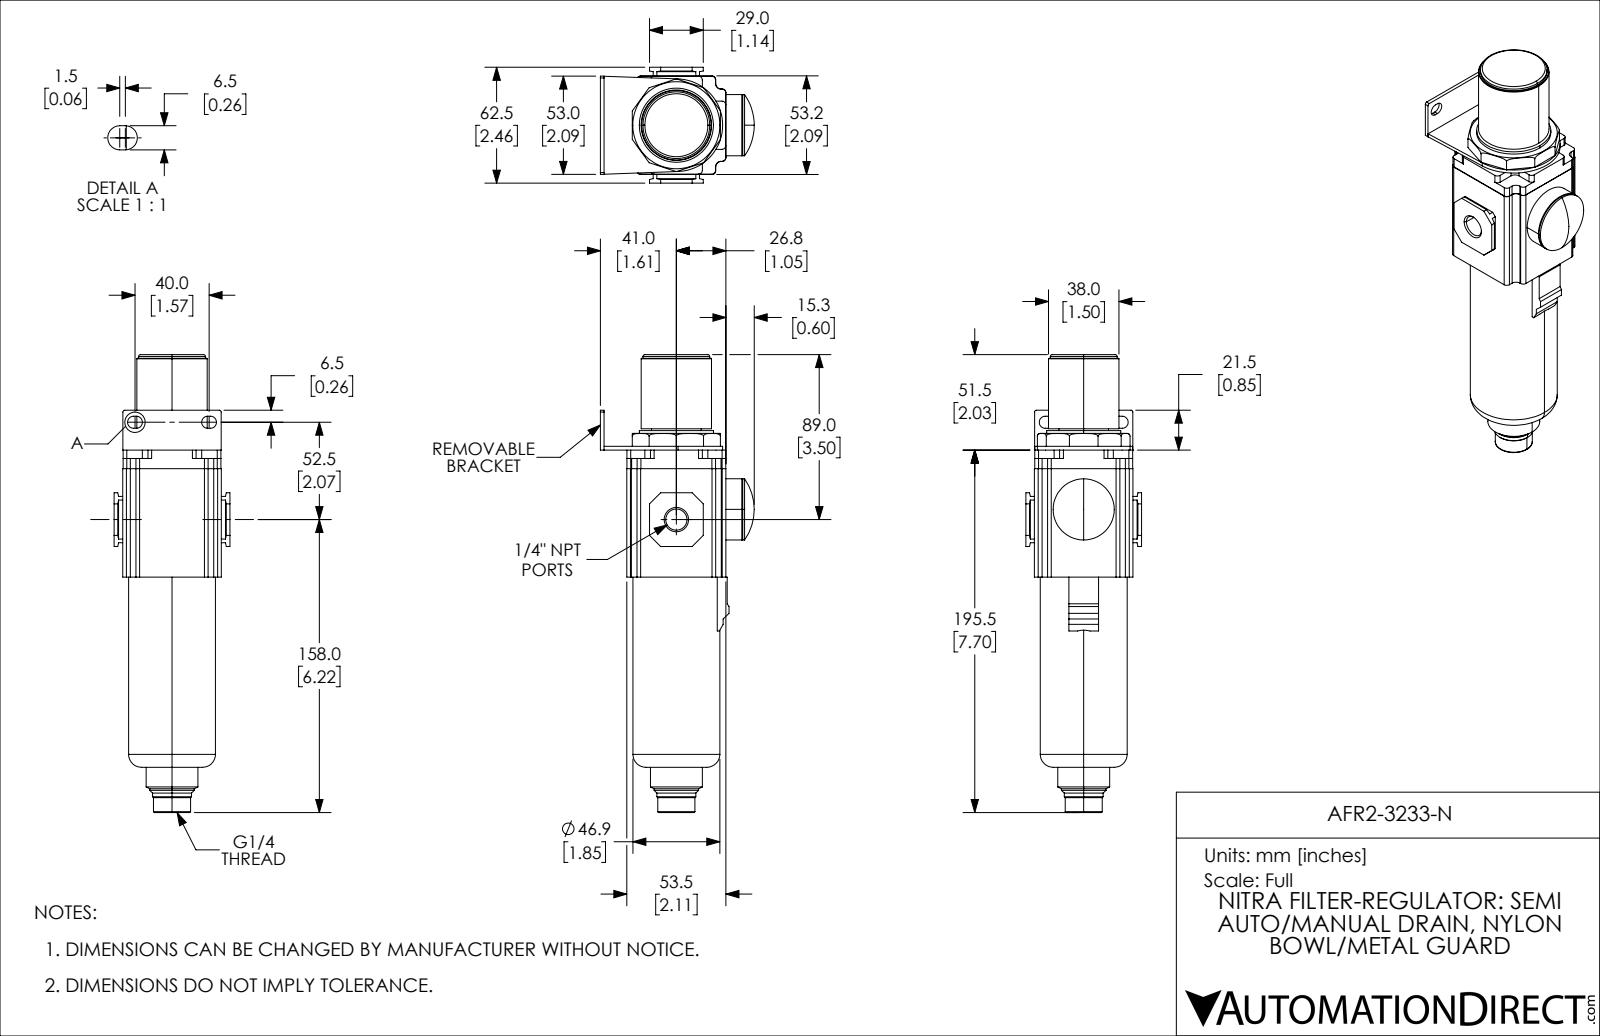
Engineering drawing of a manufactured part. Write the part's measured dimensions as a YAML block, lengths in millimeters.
part_name: "AFR2-3233-N"
step_written_by: "SolidWorks 2019 (CONFIG_CONTROL_DESIGN)"
units: millimeters
bodies: {solids: 1, faces: 221, planar: 124, cylindrical: 71, other: 26}
overall_size: [247, 83.03, 62.5]
volume: 452721
surface_area: 51631
round_holes:
  - {diameter: 11.45, count: 2}
round_bosses_or_shafts:
  - {diameter: 46.9, count: 1}
  - {diameter: 40, count: 1}
  - {diameter: 38, count: 1}
  - {diameter: 36, count: 1}
  - {diameter: 33, count: 1}
  - {diameter: 28, count: 1}
  - {diameter: 26.78, count: 1}
  - {diameter: 24, count: 1}
partial_cylinders:
  - {radius: 2, count: 24}
  - {radius: 3, count: 12}
  - {radius: 3.25, count: 4}
  - {radius: 1, count: 2}
  - {radius: 25, count: 1}
face_to_face_distances: [2, 53.2, 53.5, 4.65, 57.85, 14.25, 12.25, 67.75, 51.5, 49.5]
